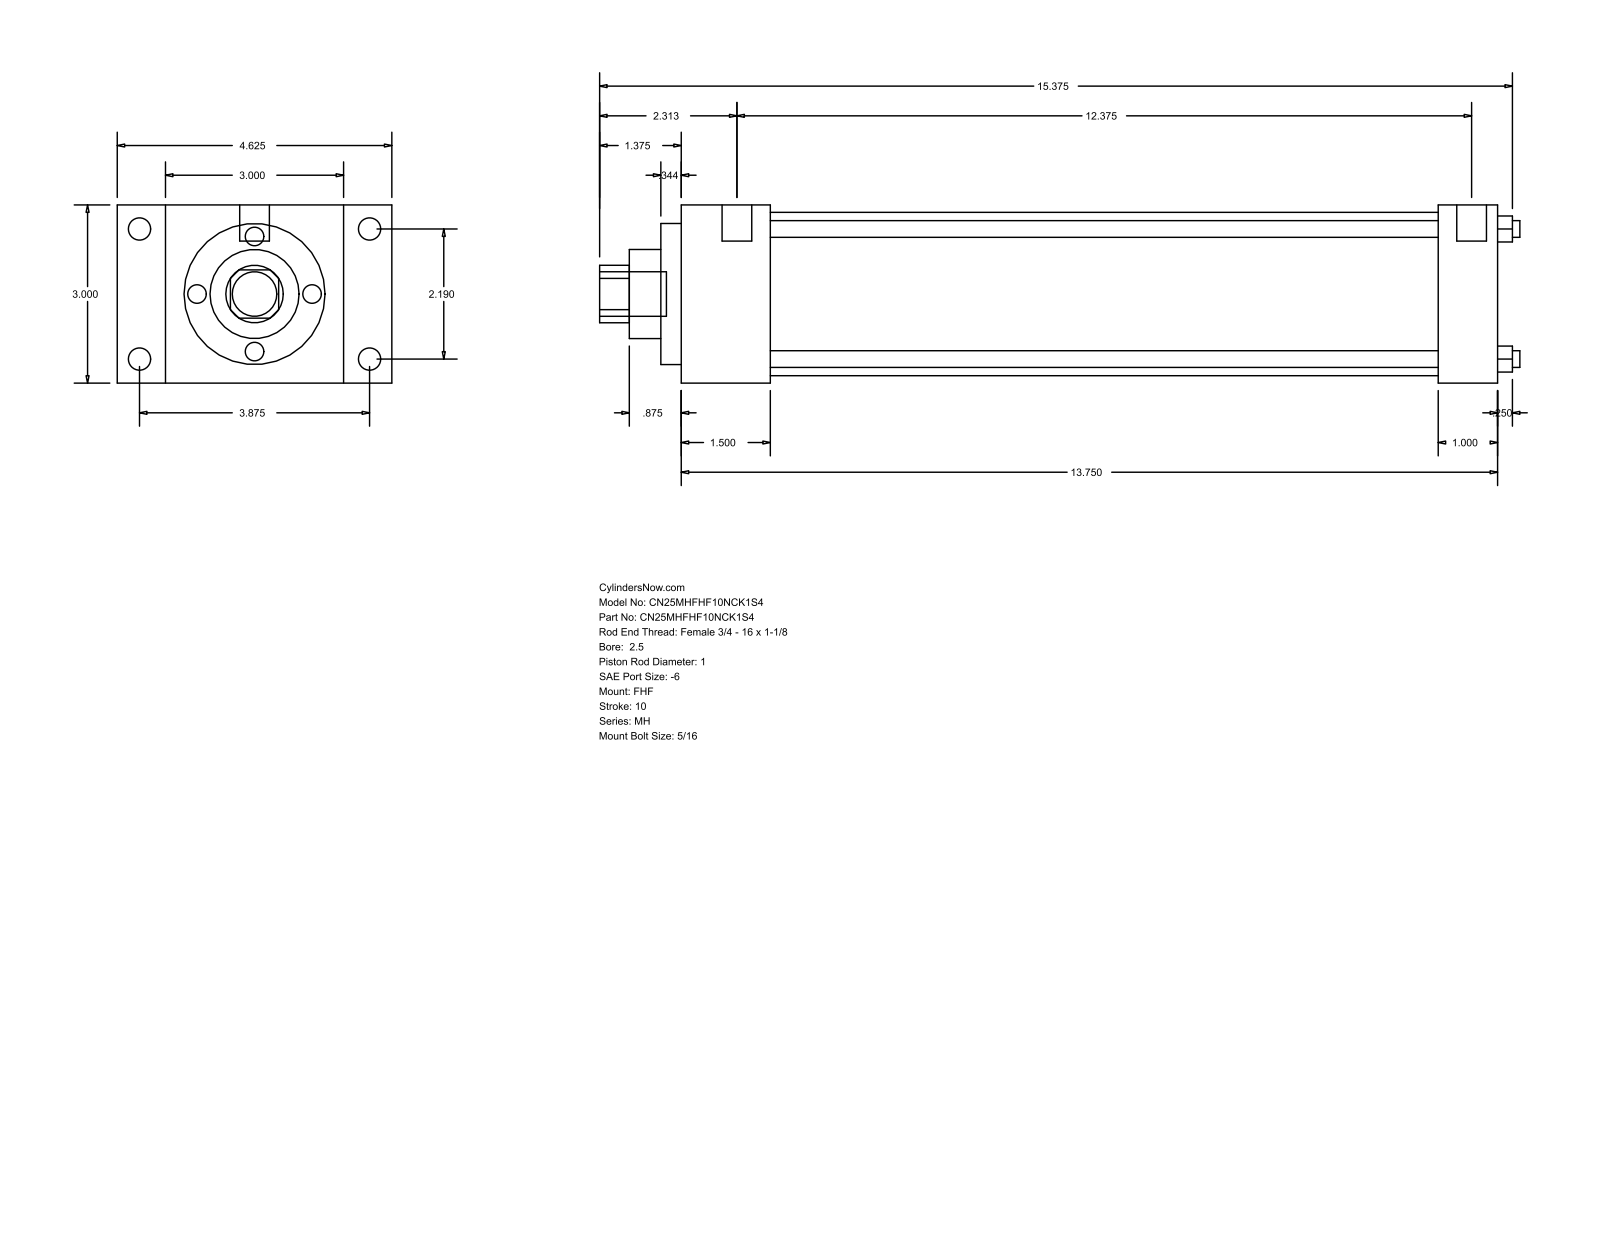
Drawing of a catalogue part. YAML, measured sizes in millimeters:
part_name: "MH_FHF__0250_1"
step_written_by: "GSSL Pune (CONFIG_CONTROL_DESIGN)"
units: millimeters
bodies: {solids: 0, faces: 90, planar: 61, cylindrical: 29, other: 0}
overall_size: [393.7, 117.47, 76.2]
round_holes:
  - {diameter: 7.14, count: 4}
  - {diameter: 25.4, count: 1}
  - {diameter: 38.1, count: 1}
  - {diameter: 60.33, count: 1}
  - {diameter: 69.85, count: 1}
round_bosses_or_shafts:
  - {diameter: 9.53, count: 4}
  - {diameter: 5.56, count: 4}
  - {diameter: 12.7, count: 2}
  - {diameter: 19.05, count: 1}
partial_cylinders:
  - {radius: 12.29, count: 1}
face_to_face_distances: [76.2, 349.26, 38.11, 311.15, 20.64, 96.84, 117.48, 323.85, 285.74, 25.41]
hole_center_spacings: [39.33, 55.62, 78.66]
